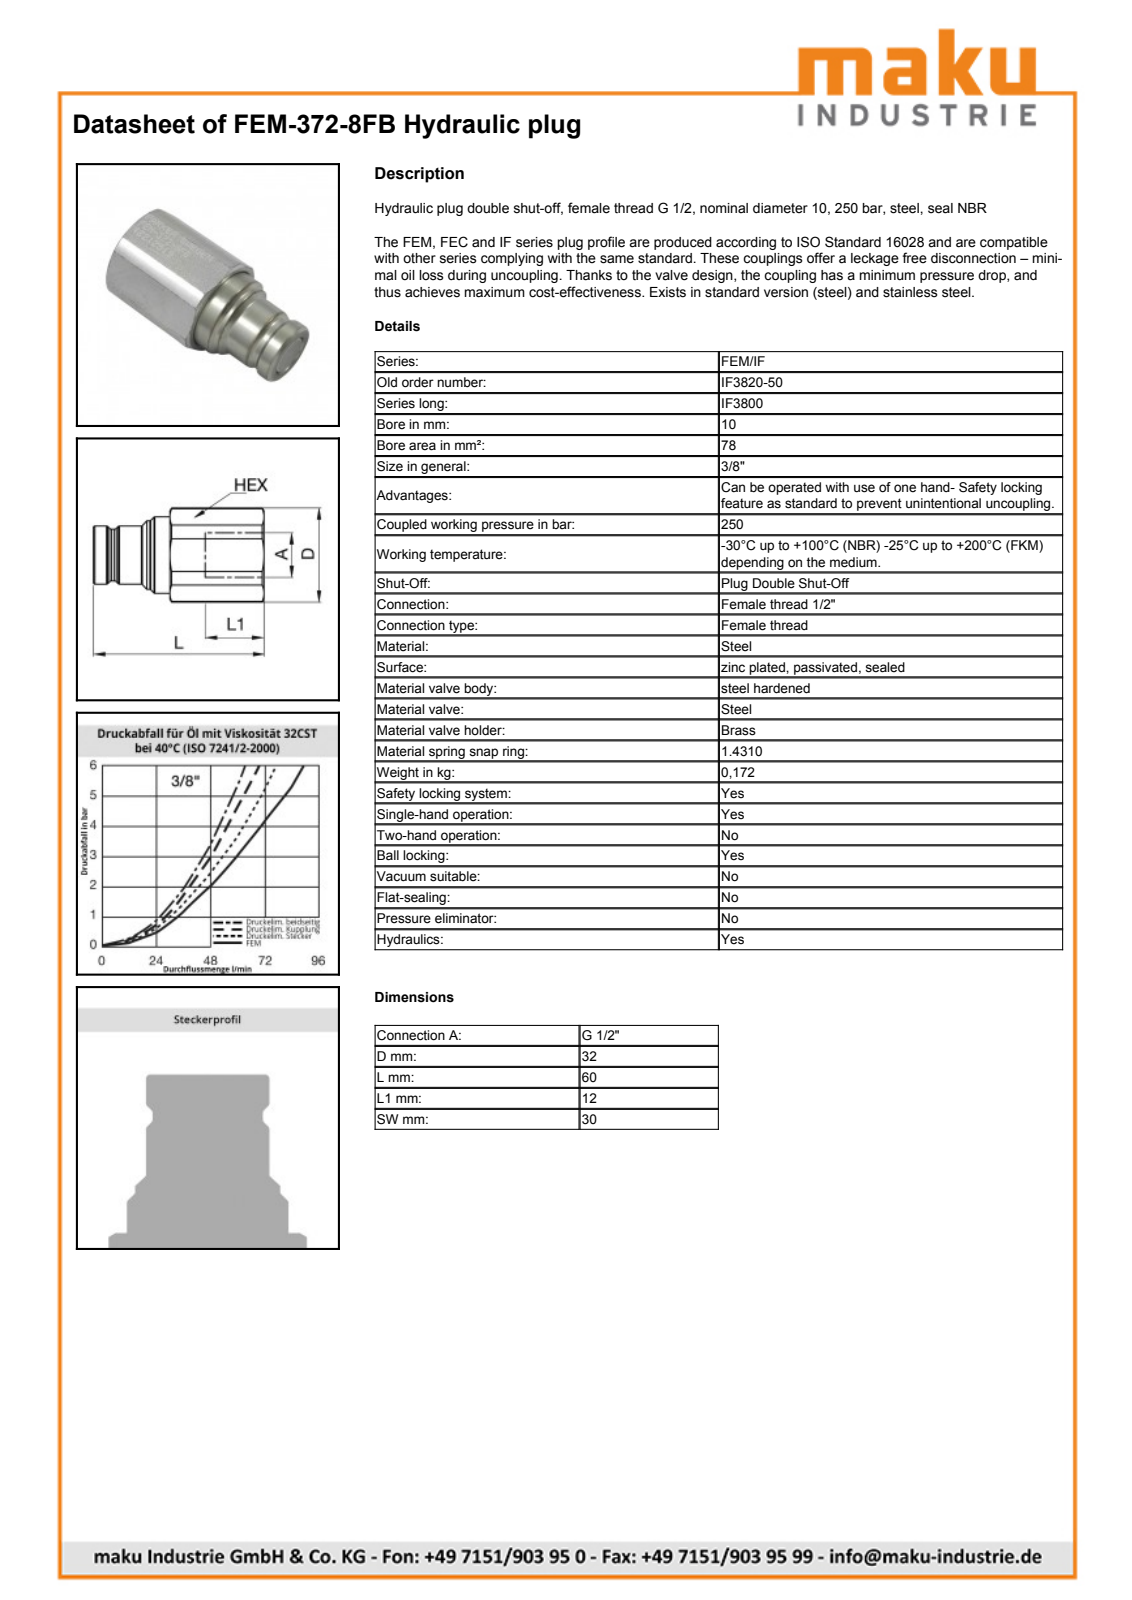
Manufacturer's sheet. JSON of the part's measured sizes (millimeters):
{"part_name": "FEM-372-8FB", "step_written_by": "SolidWorks 2009 (AUTOMOTIVE_DESIGN)", "units": "millimeters", "bodies": {"solids": 1, "faces": 77, "planar": 13, "cylindrical": 24, "other": 40}, "overall_size": [60, 32, 30], "volume_mm3": 29966, "surface_area_mm2": 7634, "round_holes": [[12.65, 1], [14.5, 1], [18.63, 1], [26.15, 1]], "round_bosses_or_shafts": [[26, 1], [23.3, 1], [19.75, 1], [17.6, 1]], "partial_cylinders_radius": [[16, 1]], "face_to_face_distances": [30, 60, 40.71, 19.29, 26, 14.71, 34, 26.7, 0.7, 14.01]}
